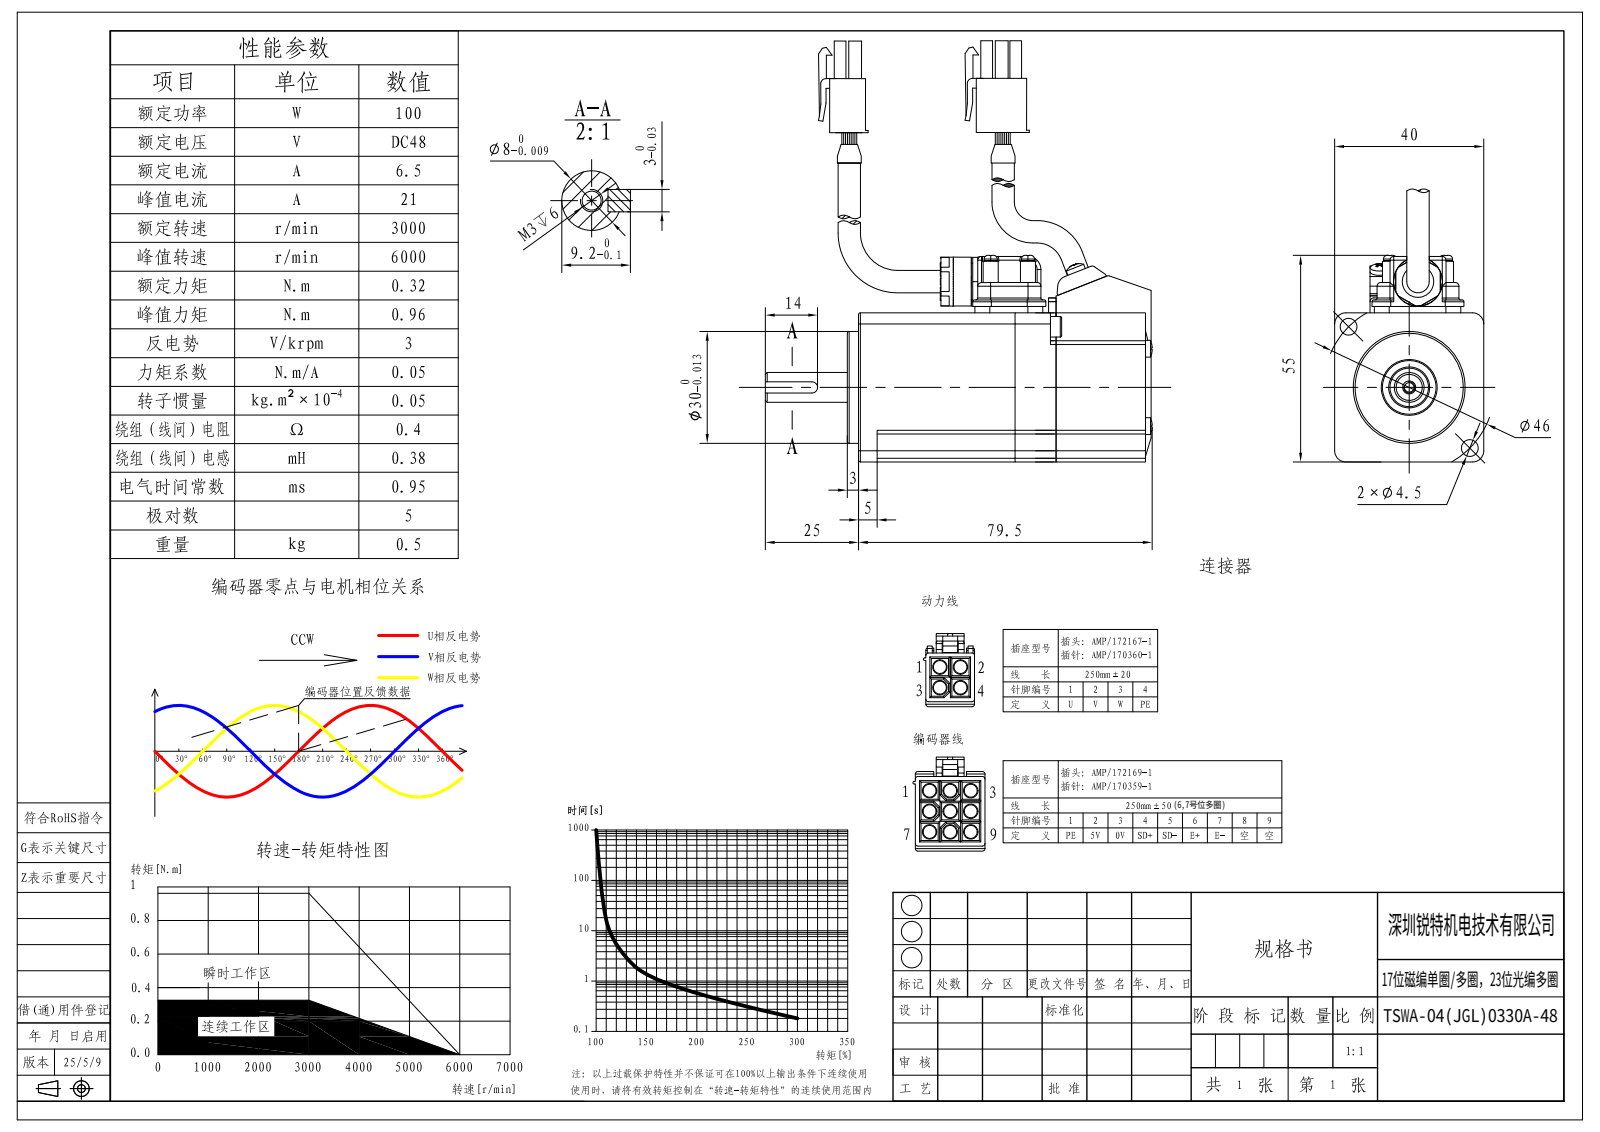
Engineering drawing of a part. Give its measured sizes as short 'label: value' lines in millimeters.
written by: SolidWorks 2018 (CONFIG_CONTROL_DESIGN)
unit: mm
bodies: 0 solids, 2267 faces (236 planar, 220 cylindrical, 1811 other)
size: 104.42 × 53.71 × 40.44
holes: 8× ⌀2.05, 7× ⌀2.5, 2× ⌀2, 2× ⌀3.5, 2× ⌀4.5, 2× ⌀10, 1× ⌀6.3, 1× ⌀7, 1× ⌀8, 1× ⌀12, 1× ⌀13.67, 1× ⌀14.5
bosses: 4× ⌀4.5, 3× ⌀5, 2× ⌀5.5, 2× ⌀3, 1× ⌀38.5, 1× ⌀30, 1× ⌀12.67, 1× ⌀10.33
rounds: 28× R0.3, 16× R1, 6× R4.5, 5× R3, 4× R0.5, 4× R2, 2× R0.8, 2× R3.25
face distances: 40, 1.5, 0.5, 35.5, 37, 7.5, 2, 3, 53.5, 11.5
hole spacings: 8, 20.75, 14.5, 6.13, 16, 26.69, 32.53, 8.18
